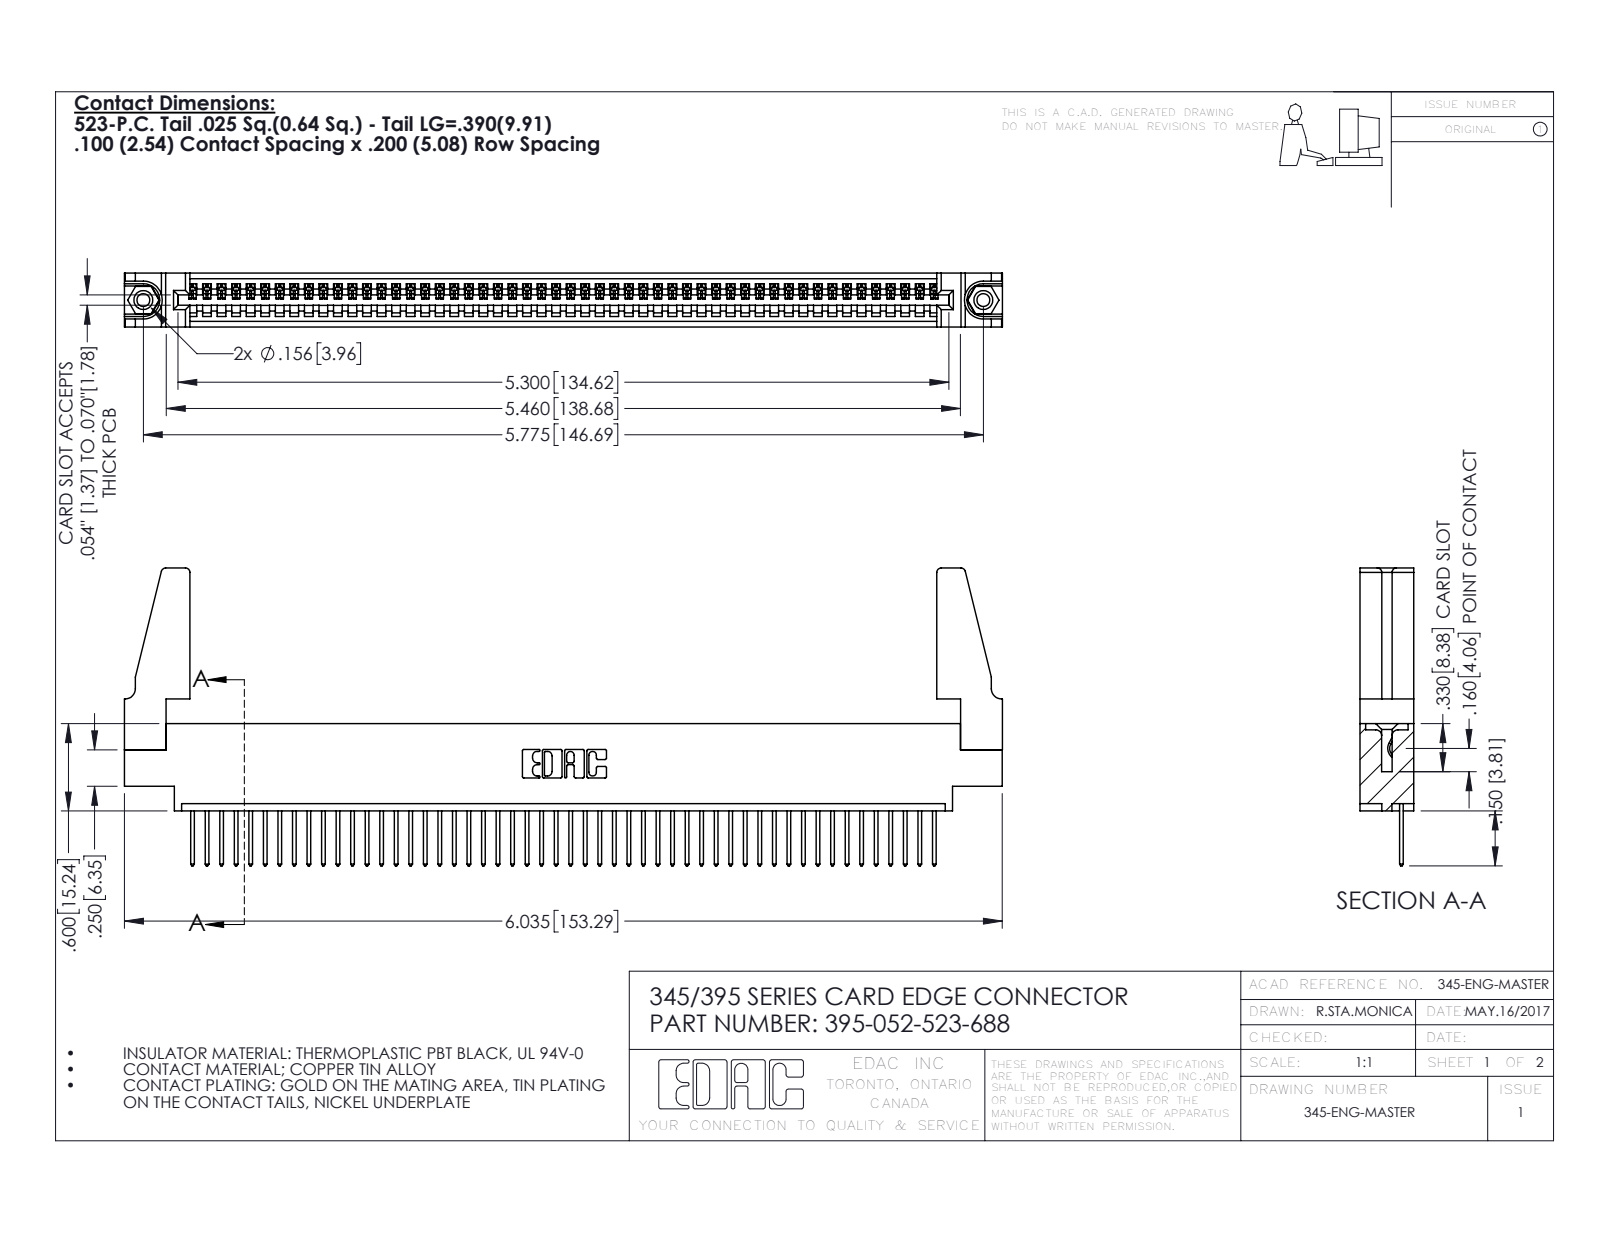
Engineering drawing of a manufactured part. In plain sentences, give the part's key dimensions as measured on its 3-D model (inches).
The part is named "395-052-523-688; 345 Part_0.170 Offset - 0.156 Dia-TH; 345-220-078_345-220-088; 345-250-001_345-250-001-102 (+1 more)". Its 3-D file was written by "SolidWorks 2016 (CONFIG_CONTROL_DESIGN)". It is 57 solids with 3270 faces: 2236 planar, 1018 cylindrical and 16 other. Overall it measures 6.036 by 2.047 by 0.37 inches. Its volume is 1.084 cubic inches and its surface area 35.23 square inches. Round holes: 2 of diameter 0.089, 2 of diameter 0.125, 2 of diameter 0.156, 1 of diameter 0.064. Round bosses or shafts: 2 of diameter 0.155. Partial cylindrical surfaces (rounded edges, fillets, slot ends): 104 of radius 0.006, 104 of radius 0.01, 22 of radius 0.01, 8 of radius 0.03, 6 of radius 0.007, 6 of radius 0.031, 3 of radius 0.026, 2 of radius 0.031. The main face-to-face distances are 0.072, 0.298, 0.37, 0.098, 0.272, 0.025, 0.2, 0.225, 0.175, 0.149. The hole center spacings are 0.27, 5.539, 5.775.
